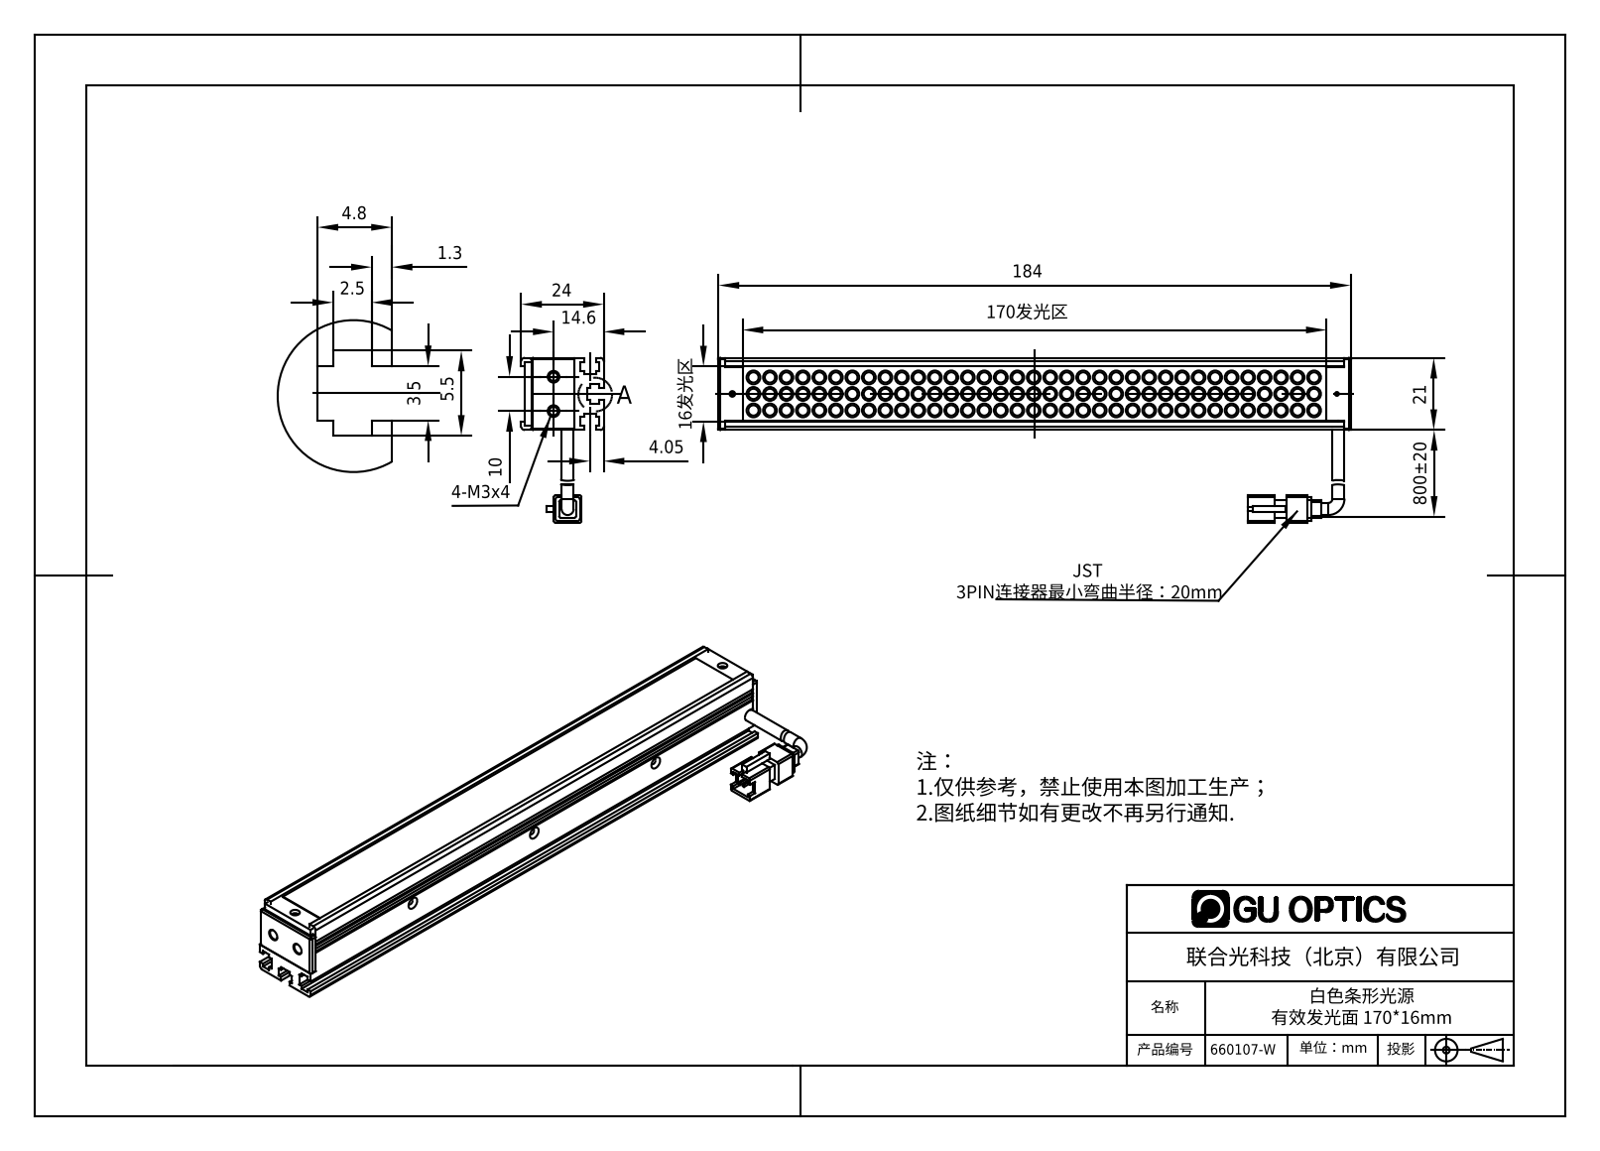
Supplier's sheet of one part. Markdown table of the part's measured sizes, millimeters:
| quantity | value |
| --- | --- |
| part name | 660107-W |
| STEP written by | SolidWorks 2016 (AUTOMOTIVE_DESIGN) |
| units | millimeters |
| bodies | 8 solids, 1075 faces (356 planar, 507 cylindrical, 212 other) |
| overall size | 184 × 48 × 24 |
| volume | 53 223 mm³ |
| surface area | 59 208 mm² |
| round holes (diameter × count) | 1.6 × 5, 1.7 × 3, 1.5 × 2, 2.5 × 2, 2.8 × 2, 3 × 2, 1.1 × 1, 1.25 × 1, 2 × 1 |
| round bosses / shafts (diameter × count) | 4 × 105, 3 × 105, 3.5 × 2 |
| partial cylindrical surfaces (radius × count) | 1 × 12, 0.5 × 8, 1.65 × 1 |
| main face-to-face distances | 1, 2.5, 2, 18.5, 21, 4, 14.6, 1.3, 2.2, 3.5 |
| hole center spacings | 176, 7, 38.03, 38.38, 50, 88.01, 88.17, 138.01 |
